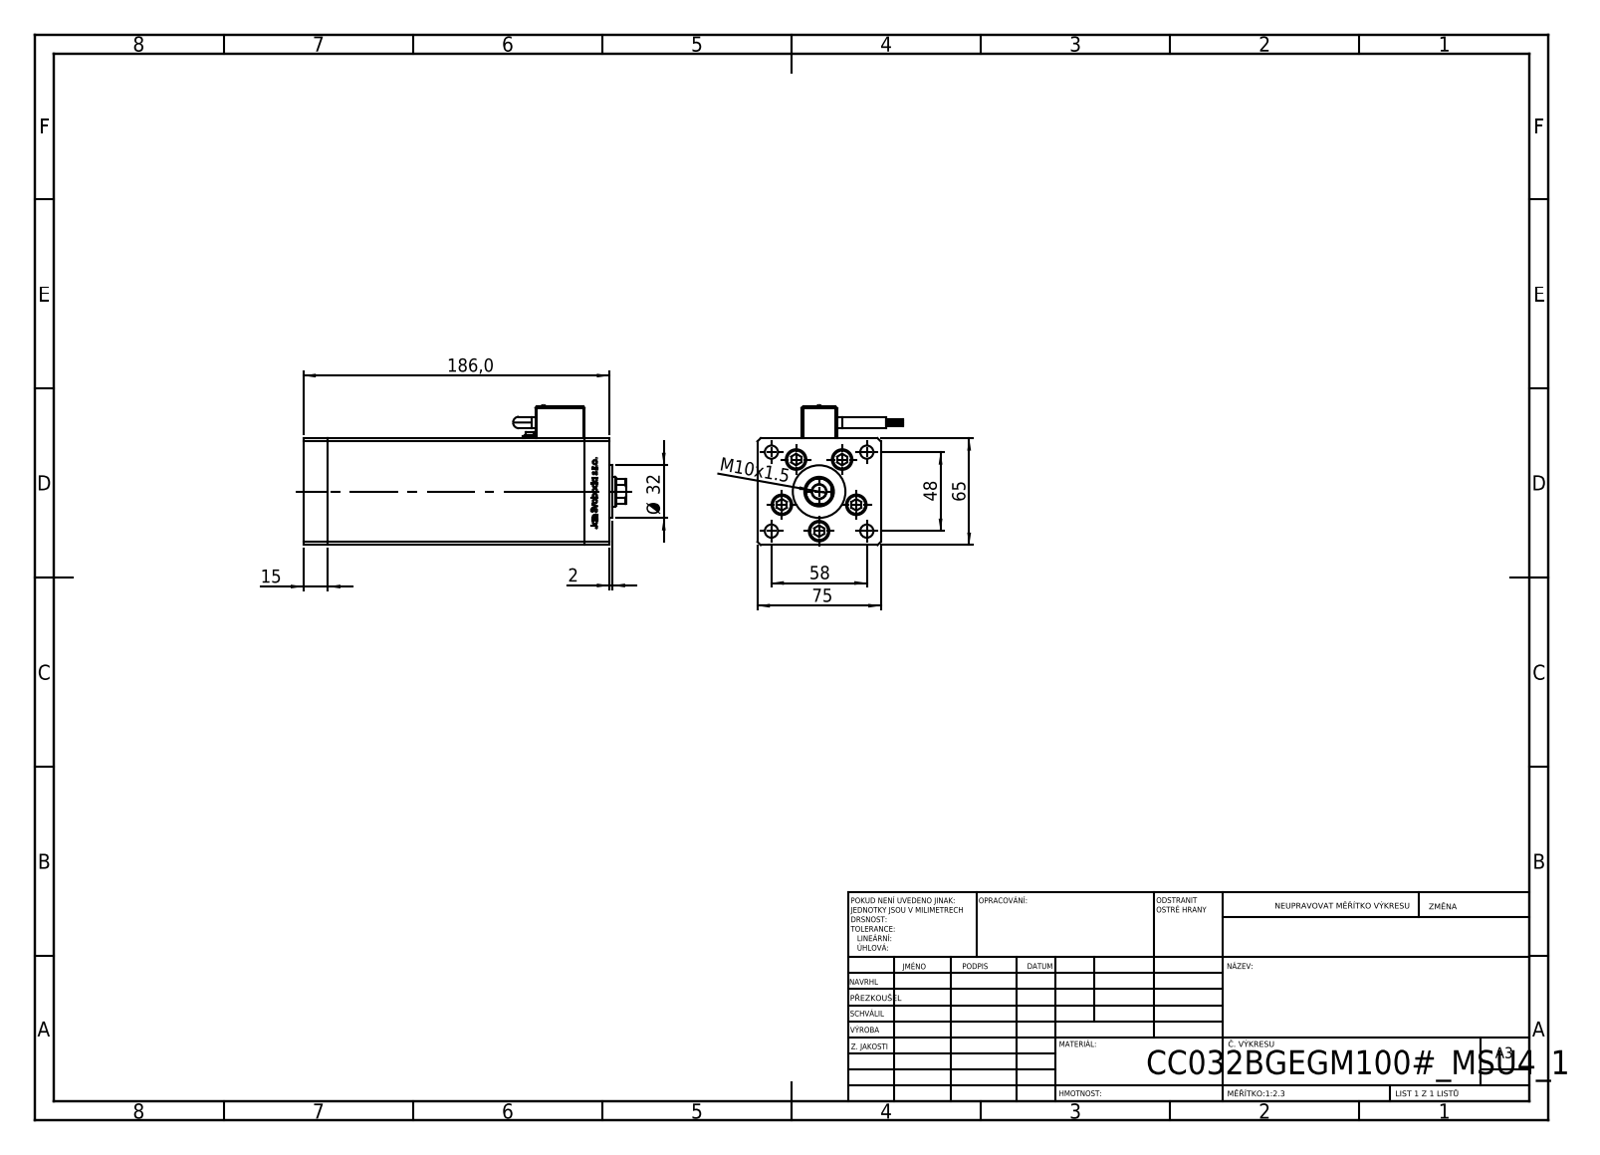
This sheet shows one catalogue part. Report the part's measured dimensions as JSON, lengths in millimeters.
{"part_name": "V220C_VC_B; V220C_B MIDDLE; Magnetic_Switch_MSU4; V220C_FRONT_B (+2 more)", "step_written_by": "SolidWorks 2019 (CONFIG_CONTROL_DESIGN)", "units": "millimeters", "bodies": {"solids": 15, "faces": 1285, "planar": 501, "cylindrical": 192, "other": 592}, "overall_size": [196, 88.3, 85.1], "volume_mm3": 823817, "surface_area_mm2": 142161, "round_holes": [[9, 5], [12.5, 5], [8, 4], [2, 2], [13.16, 2], [3.6, 1], [5, 1], [7, 1], [8.5, 1], [18, 1]], "round_bosses_or_shafts": [[8, 5], [0.85, 4], [7, 2], [32, 1], [6, 1], [3.5, 1], [2.5, 1]], "partial_cylinders_radius": [[1, 14], [0.93, 2], [4, 2], [8.5, 1]], "face_to_face_distances": [75, 65, 15, 156, 171, 186, 4, 54.5, 10.5, 58.5], "hole_center_spacings": [24, 37.64, 15.67, 17.22, 27.71, 28.83, 29, 32.63]}
